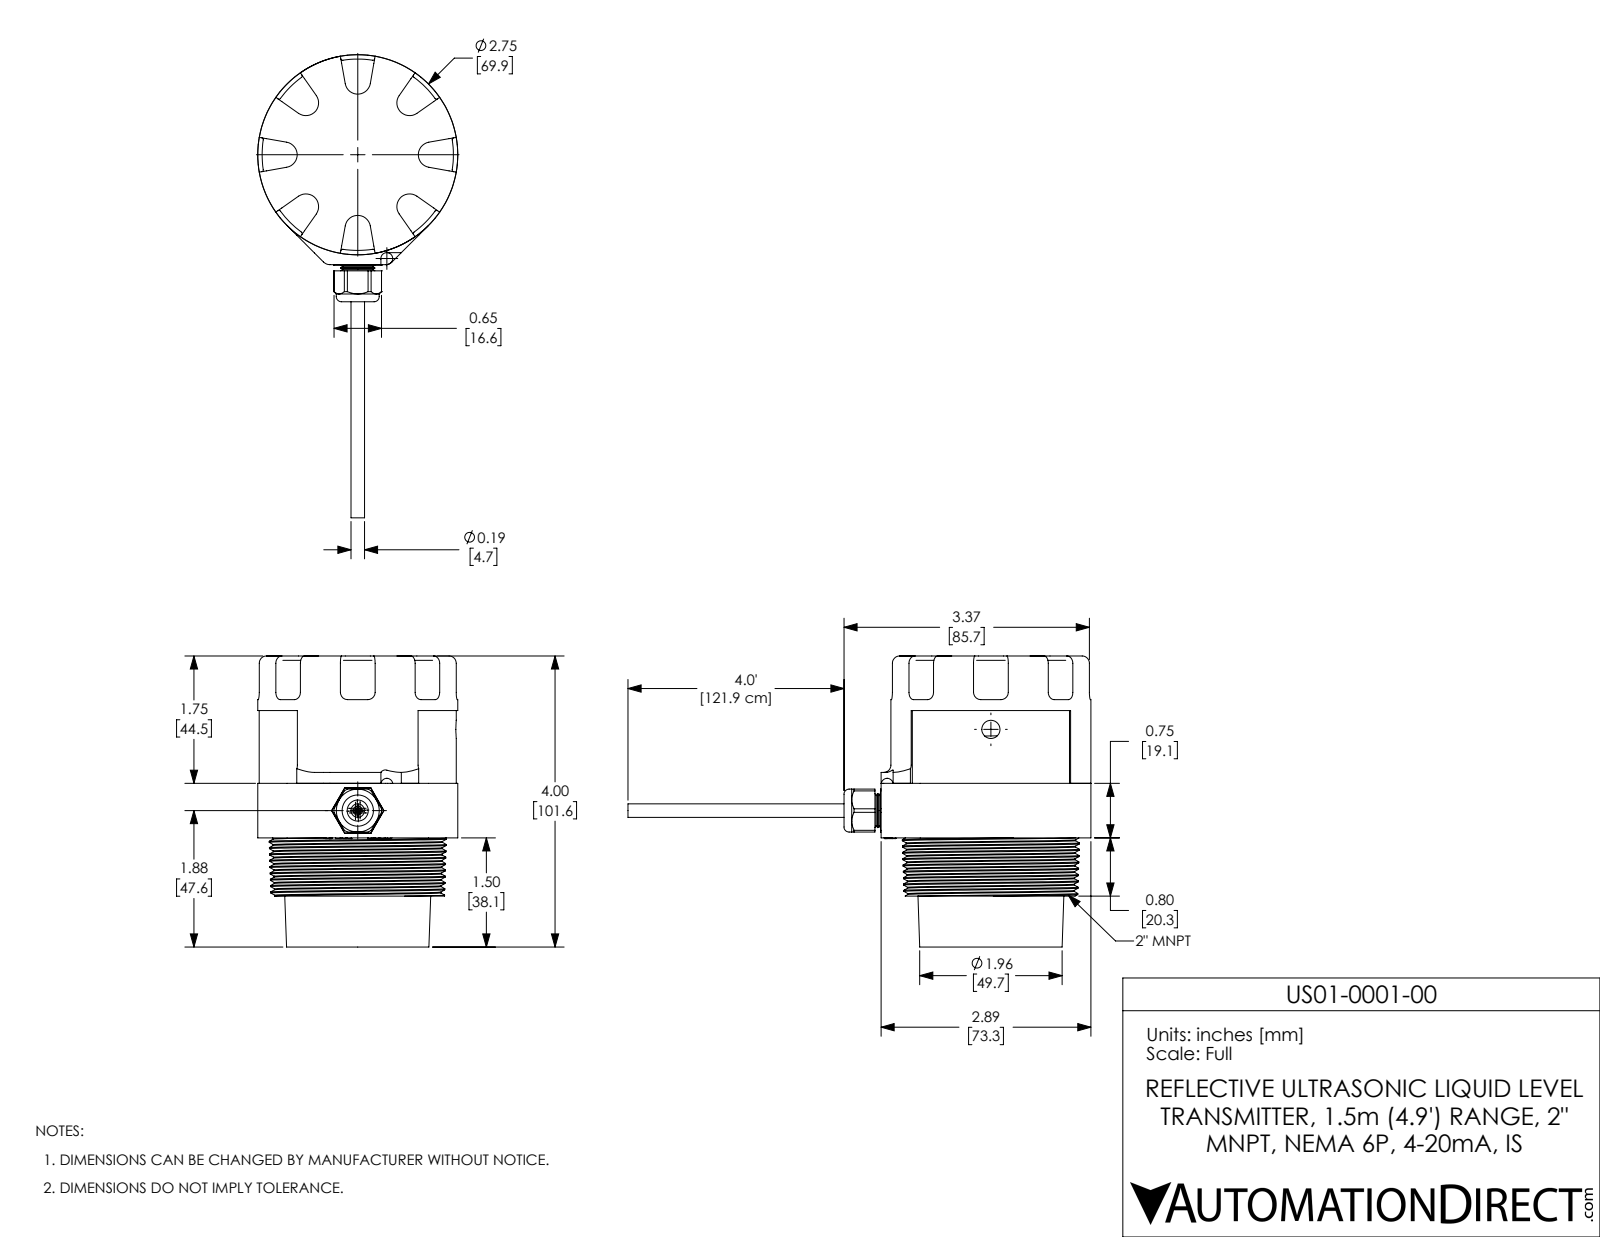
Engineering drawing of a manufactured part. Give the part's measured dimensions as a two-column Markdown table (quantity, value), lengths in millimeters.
| quantity | value |
| --- | --- |
| part name | US01-0001-00 |
| STEP written by | SolidWorks 2017 (AUTOMOTIVE_DESIGN) |
| units | millimeters |
| bodies | 11 solids, 772 faces (253 planar, 167 cylindrical, 352 other) |
| overall size | 126.2 × 126.2 × 101.6 |
| volume | 142 000 mm³ |
| surface area | 81 870 mm² |
| round holes (diameter × count) | 2.2 × 1, 3.2 × 1, 6.4 × 1, 7.4 × 1, 10.9 × 1, 48.3 × 1, 57 × 1, 59.6 × 1, 65.7 × 1 |
| round bosses / shafts (diameter × count) | 1.1 × 4, 69.9 × 1, 60 × 1, 56.7 × 1, 43.8 × 1, 42.3 × 1, 15 × 1, 4.7 × 1 |
| partial cylindrical surfaces (radius × count) | 0.6 × 32, 2.5 × 16, 4.4 × 8, 3.2 × 2, 2.1 × 1, 8.3 × 1, 22.9 × 1, 33.4 × 1 |
| main face-to-face distances | 6.4, 44.5, 38.1, 19.1, 63.5, 57.2, 0.9, 0.9, 31.8, 12.7 |
| hole center spacings | 37.6 |
